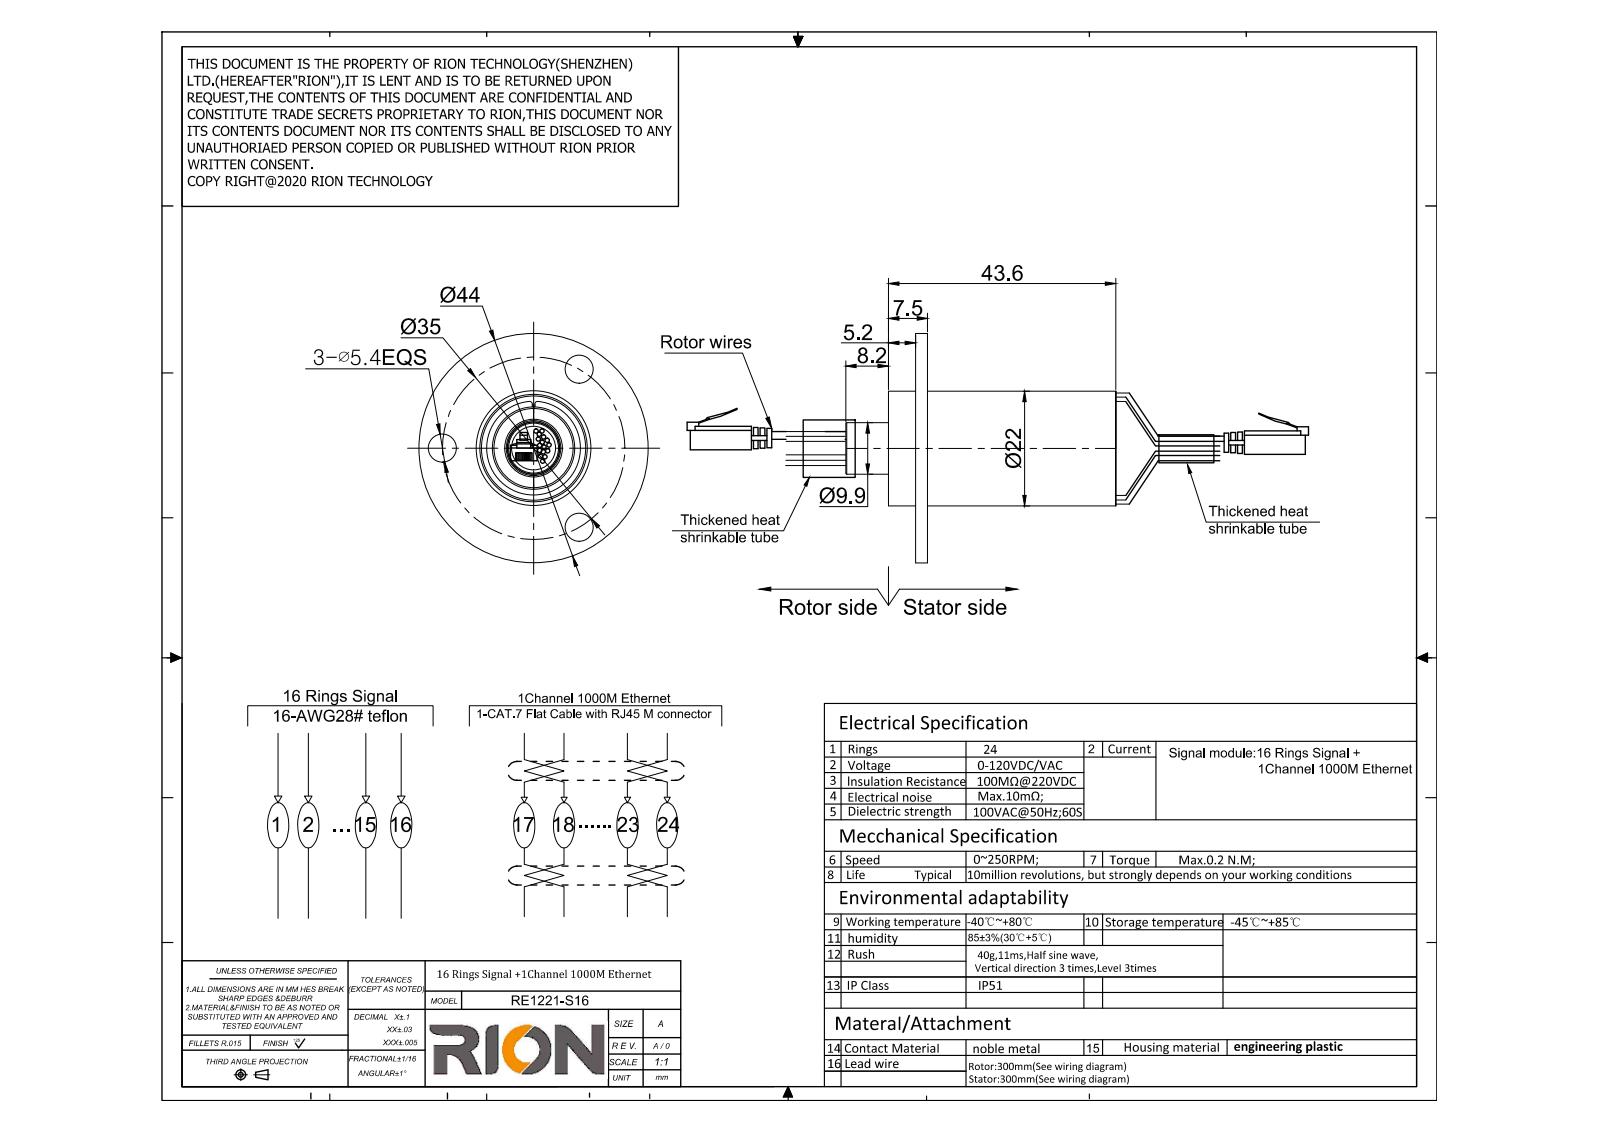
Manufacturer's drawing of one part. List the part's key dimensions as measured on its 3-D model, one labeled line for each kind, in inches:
Part name (STEP PRODUCT): Admi4F30FF6Cyqug
STEP written by: SIEMENS PLM Software NX 8.5 (AUTOMOTIVE_DESIGN)
Units: inches
Bodies: 1 solid, 228 faces (144 planar, 84 cylindrical, 0 other)
Overall size (bounding box): 4.378 × 1.732 × 1.732
Volume: 1.28 in³ · Surface area: 14 in²
Round holes (diameter × count): ⌀0.213 ×3, ⌀0.236 ×1, ⌀0.795 ×1
Round bosses / shafts (diameter × count): ⌀0.031 ×32, ⌀1.732 ×1, ⌀0.866 ×1, ⌀0.787 ×1, ⌀0.39 ×1
Main face-to-face distances: 0.091, 1.512, 1.421, 0.205, 0.295, 1.717, 0.236, 0.202, 3.012, 0.042
Hole centre spacings: 0.689, 1.193, 1.194
